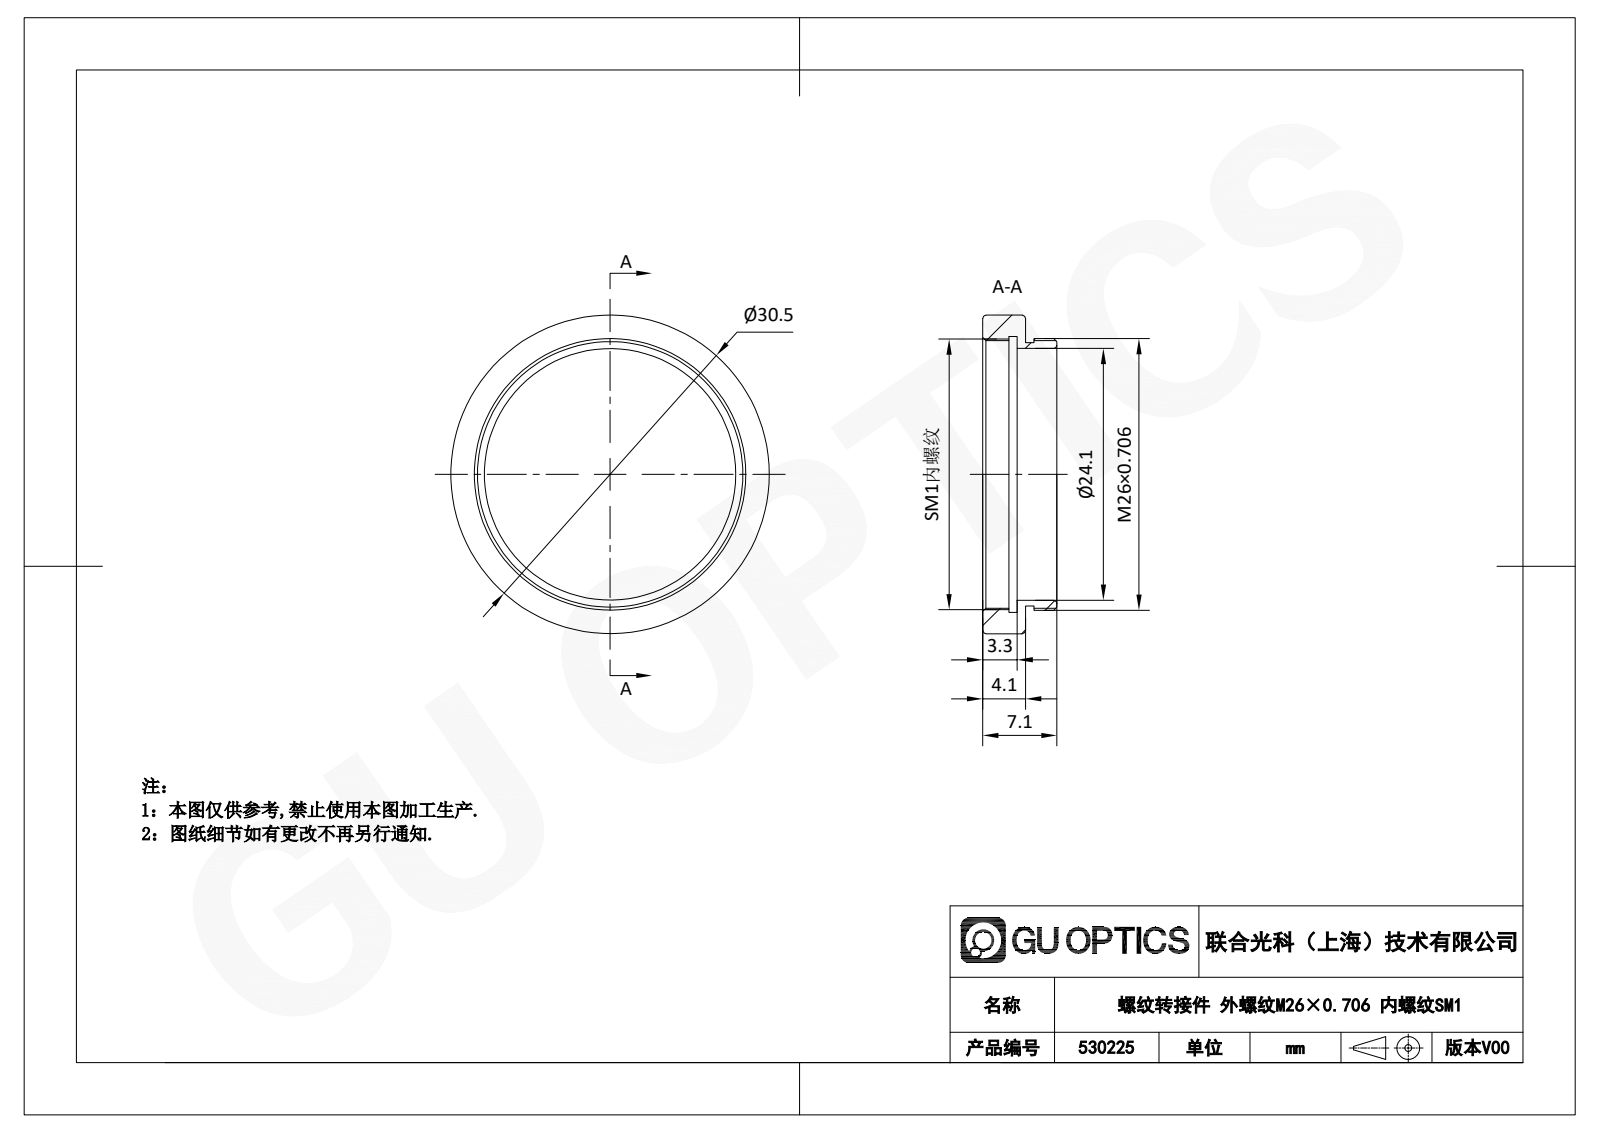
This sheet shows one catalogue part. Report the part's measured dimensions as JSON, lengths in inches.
{"part_name": "530225", "step_written_by": "SolidWorks 2020 (CONFIG_CONTROL_DESIGN)", "units": "inches", "bodies": {"solids": 1, "faces": 17, "planar": 6, "cylindrical": 6, "other": 5}, "overall_size": [1.201, 1.201, 0.28], "volume_in3": 0.067, "surface_area_in2": 2.801, "round_holes": [[0.949, 1], [1.008, 1], [1.039, 1]], "round_bosses_or_shafts": [[1.201, 1], [1.024, 1], [0.992, 1]], "face_to_face_distances": [0.161, 0.031, 0.13, 0.063, 0.098, 0.193, 0.094, 0.28, 0.181, 0.15]}
